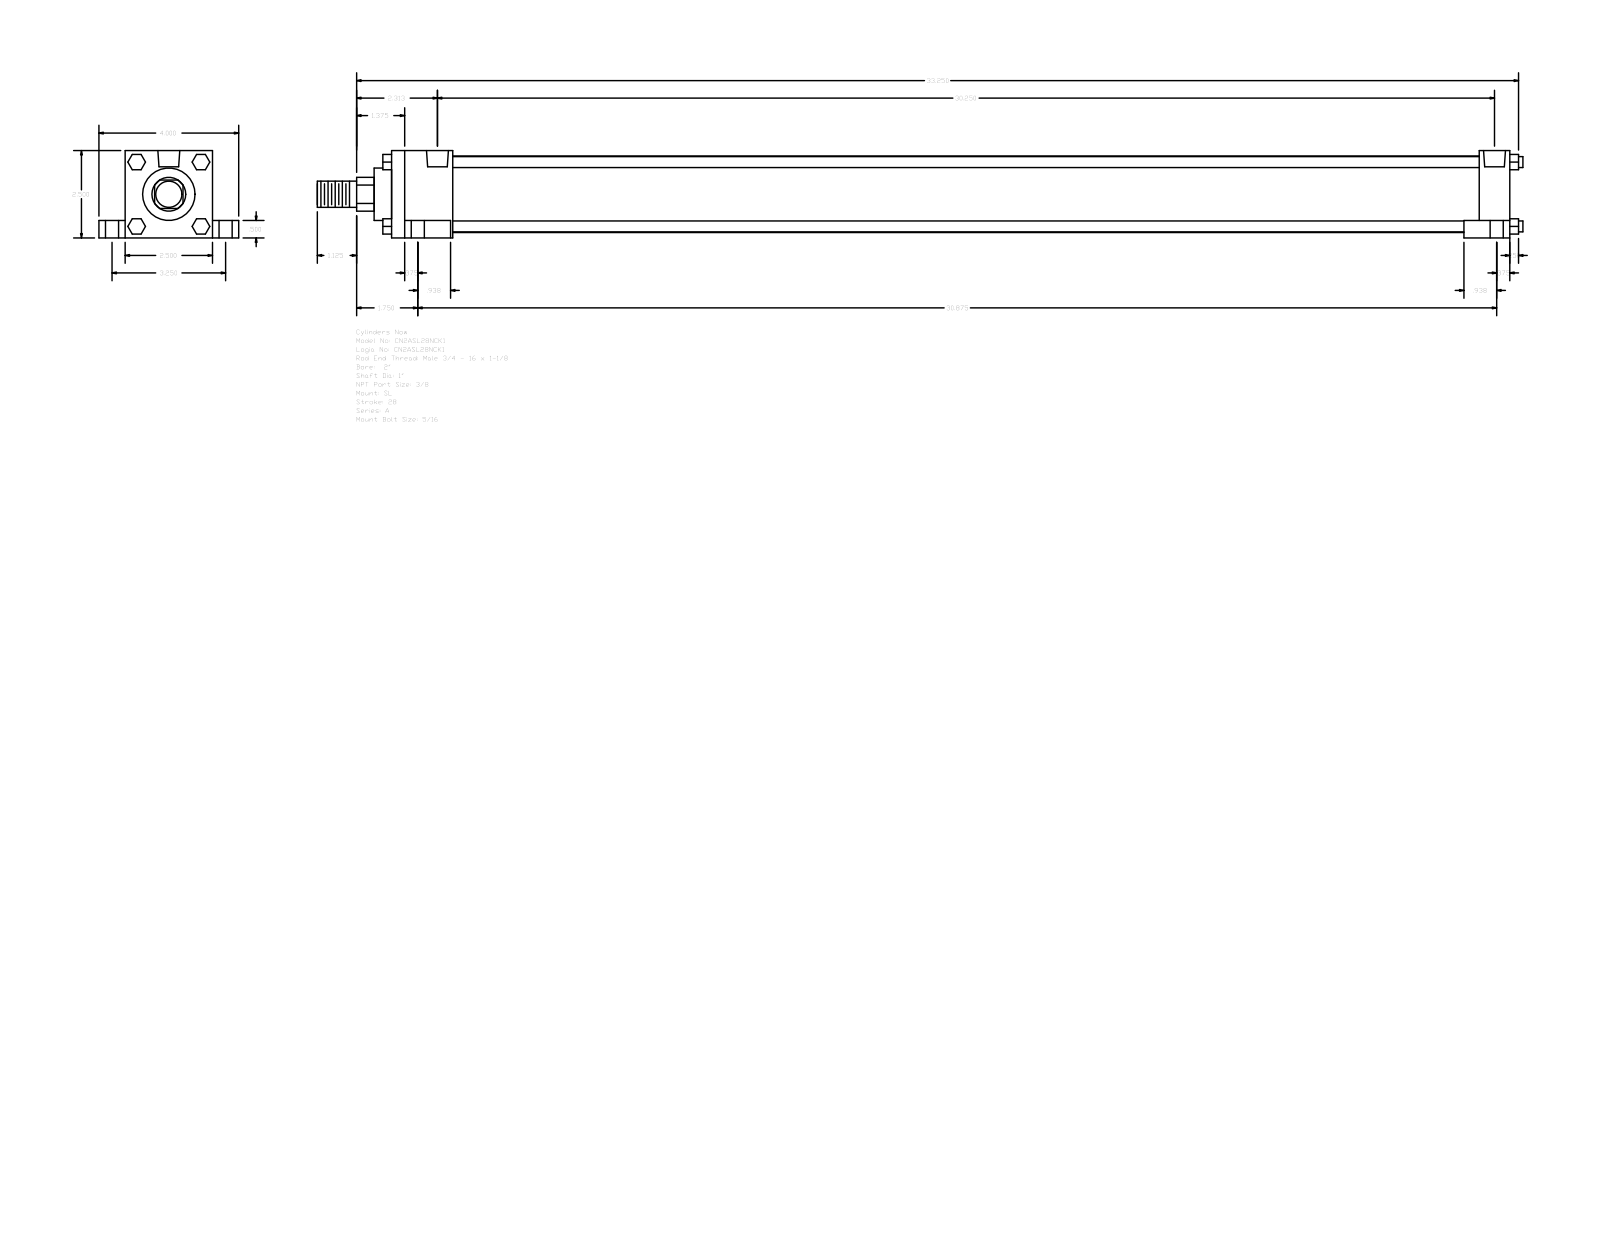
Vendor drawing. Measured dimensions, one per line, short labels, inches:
name: A_SL__0200_1
written by: GSSL Pune (CONFIG_CONTROL_DESIGN)
unit: in
bodies: 0 solids, 148 faces (112 planar, 36 cylindrical, 0 other)
size: 34.5 × 4 × 2.5
holes: 4× ⌀0.219, 4× ⌀0.375, 4× ⌀0.625, 2× ⌀0.627
bosses: 4× ⌀0.313, 1× ⌀2.19, 1× ⌀1.5, 1× ⌀1, 1× ⌀0.75
rounds: 1× R0.484
face distances: 2.5, 0.5, 32, 2, 0.875, 0.75, 3.25, 1.75, 30.25, 31.125
hole spacings: 1.626, 1.639, 1.719, 1.741, 3.25, 30.031, 30.293, 30.356
